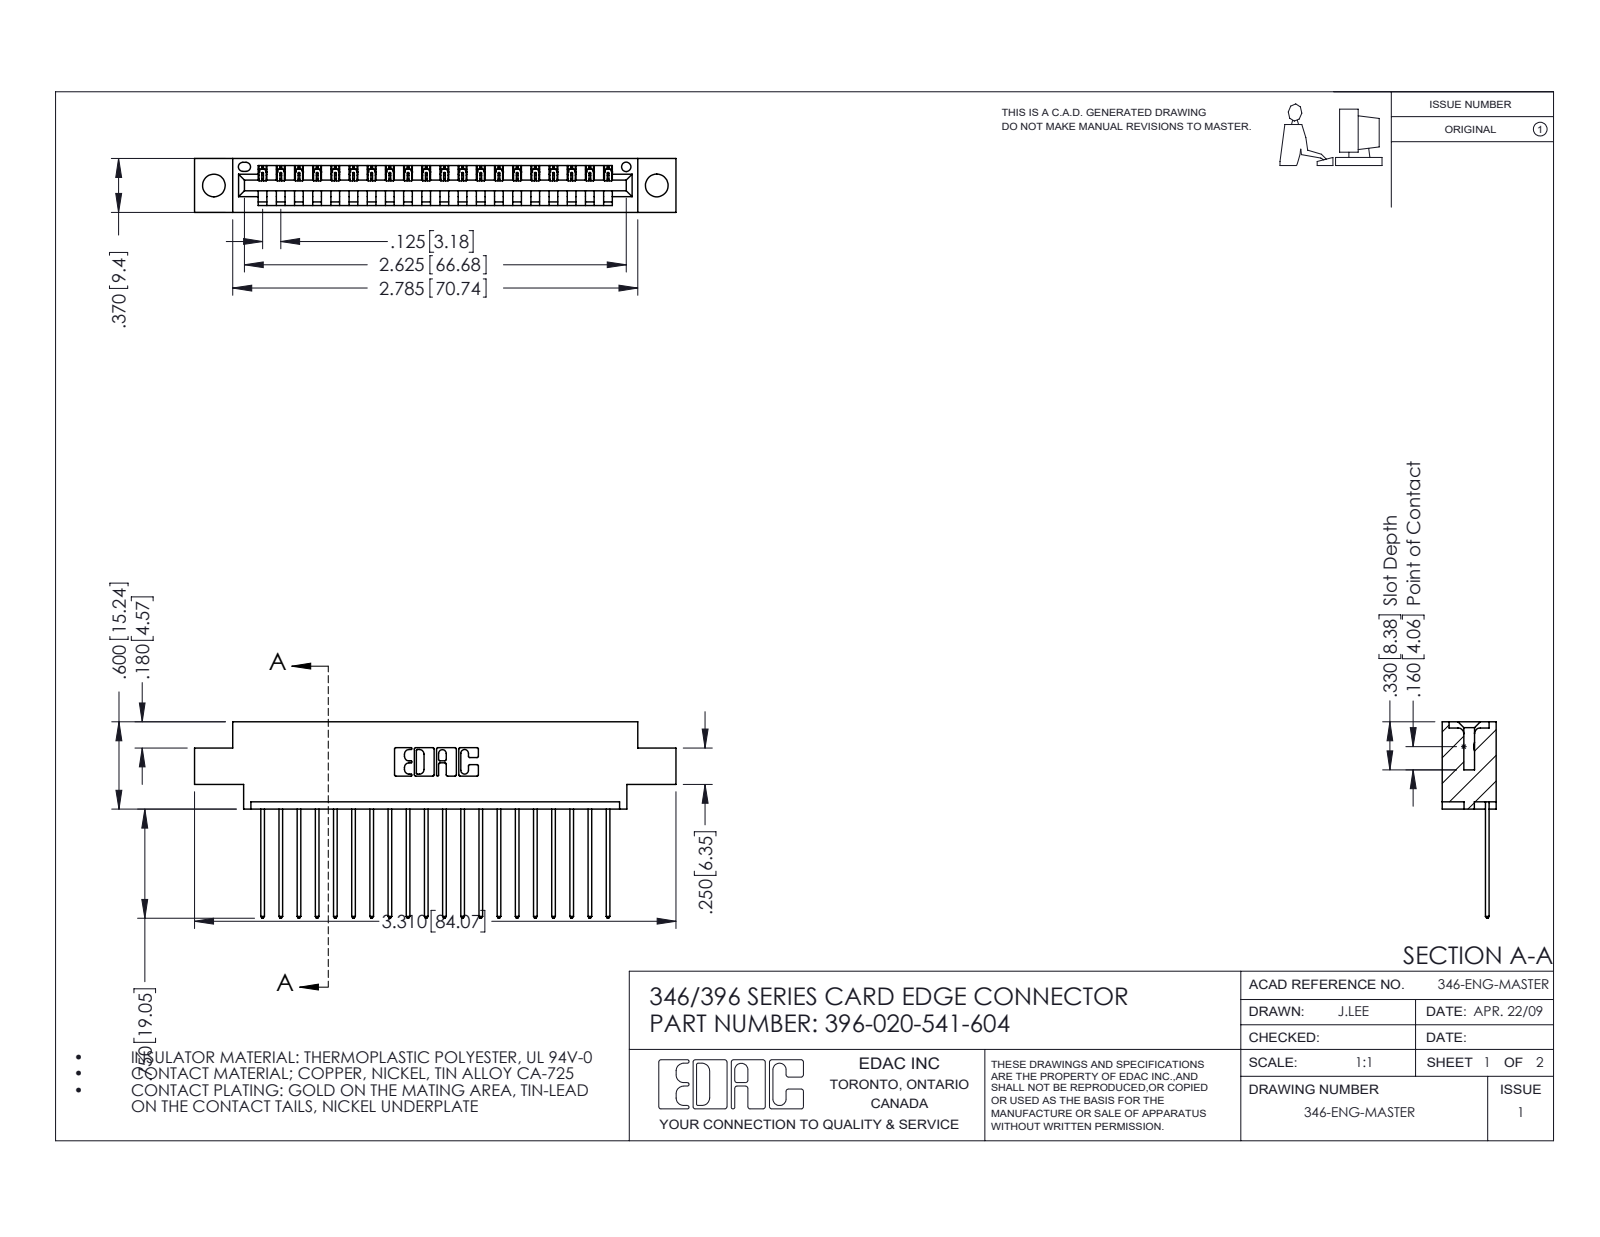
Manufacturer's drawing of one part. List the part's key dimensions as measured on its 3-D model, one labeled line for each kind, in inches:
Part name (STEP PRODUCT): 346 Part_0.170 Offset - 0.156 Dia-TH; 345-292-001_345-293-141; 396-020-541-604
STEP written by: SolidWorks 2016 (CONFIG_CONTROL_DESIGN)
Units: inches
Bodies: 21 solids, 1286 faces (880 planar, 406 cylindrical, 0 other)
Overall size (bounding box): 3.31 × 1.35 × 0.37
Volume: 0.471 in³ · Surface area: 15.14 in²
Round holes (diameter × count): ⌀0.156 ×2, ⌀0.064 ×1
Partial cylindrical surfaces — rounded edges, fillets, slot ends (radius × count): R0.006 ×40, R0.01 ×40, R0.01 ×22, R0.007 ×6, R0.031 ×6, R0.026 ×3, R0.031 ×2, R0.04 ×2
Main face-to-face distances: 0.048, 0.322, 0.37, 0.25, 0.072, 0.298, 0.025, 0.148, 0.222, 0.1
Hole centre spacings: 0.246, 2.837, 3.045
